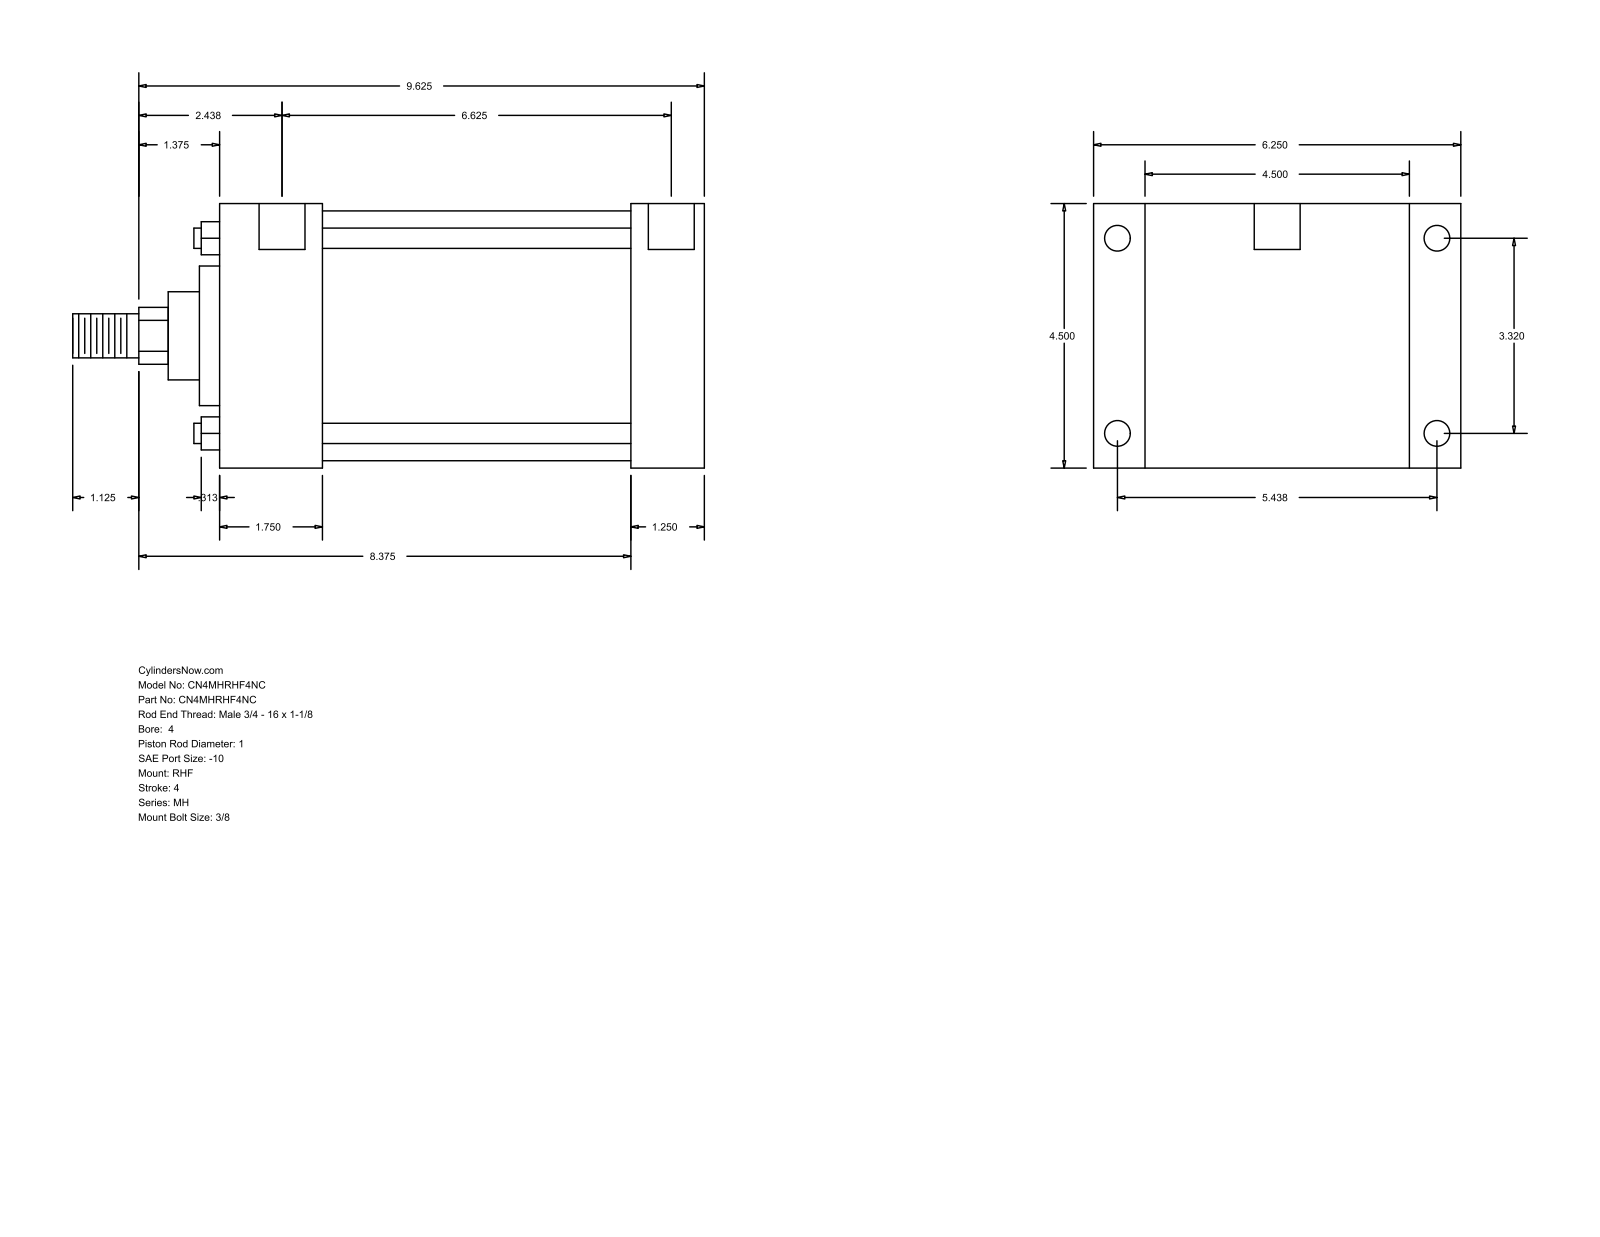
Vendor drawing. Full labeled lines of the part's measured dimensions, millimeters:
Part name (STEP PRODUCT): MH_RHF__0400_1
STEP written by: GSSL Pune (CONFIG_CONTROL_DESIGN)
Units: millimetres
Bodies: 0 solids, 90 faces (61 planar, 29 cylindrical, 0 other)
Overall size (bounding box): 273.05 × 158.75 × 114.3
Round holes (diameter × count): ⌀8.73 ×4, ⌀11.13 ×4, ⌀19.84 ×2
Round bosses / shafts (diameter × count): ⌀8.76 ×4, ⌀107.95 ×1, ⌀60.33 ×1, ⌀38.1 ×1, ⌀25.4 ×1, ⌀19.05 ×1
Partial cylindrical surfaces — rounded edges, fillets, slot ends (radius × count): R12.29 ×1
Main face-to-face distances: 114.3, 209.55, 177.8, 31.75, 22.23, 136.53, 44.46, 133.34, 165.09, 158.76
Hole centre spacings: 84.32, 138.12, 161.82, 171.45, 1.58, 1.59, 168.28, 169.86
